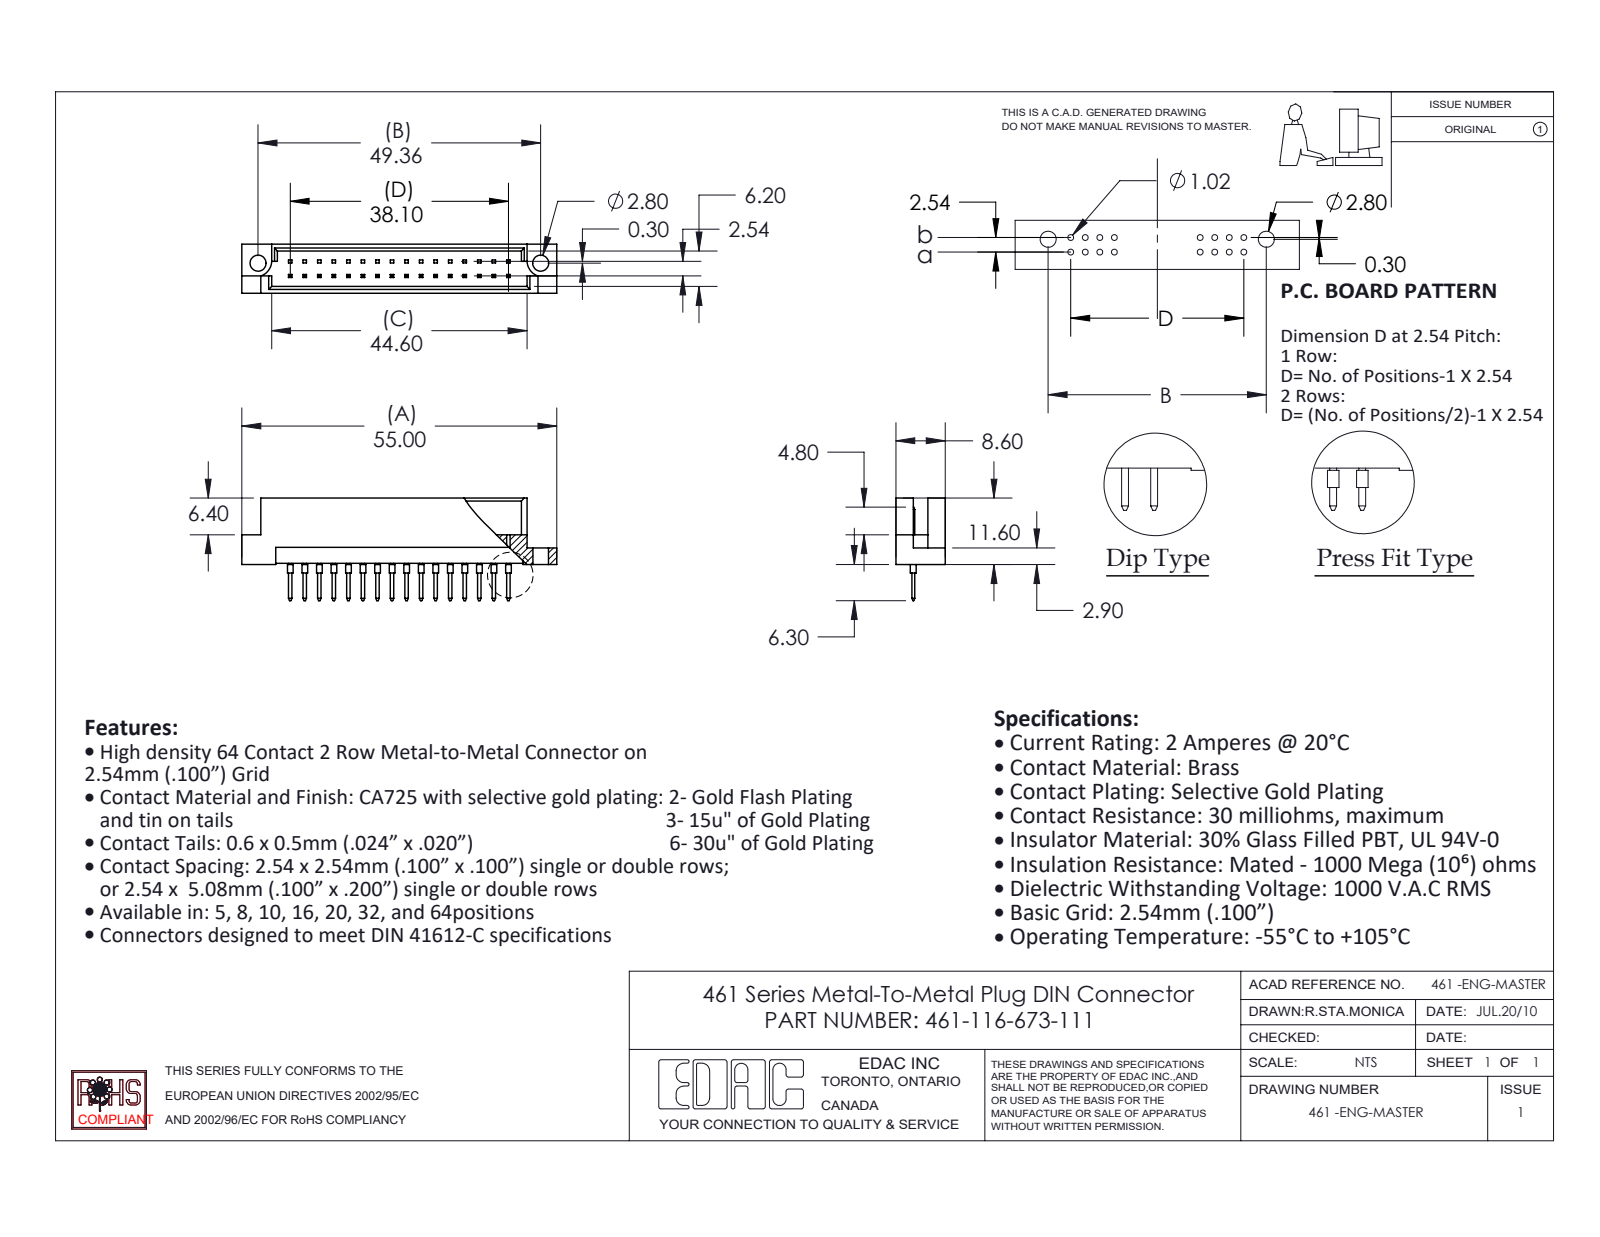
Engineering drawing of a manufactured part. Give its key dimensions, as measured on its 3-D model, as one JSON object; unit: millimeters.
{"part_name": "461-290_73; 461 Part_32; 461-116-673-111", "step_written_by": "SolidWorks 2020 (CONFIG_CONTROL_DESIGN)", "units": "millimeters", "bodies": {"solids": 17, "faces": 528, "planar": 490, "cylindrical": 38, "other": 0}, "overall_size": [55, 17.9, 8.6], "volume_mm3": 2742, "surface_area_mm2": 3854, "round_holes": [[2.8, 2]], "round_bosses_or_shafts": [[1, 16]], "partial_cylinders_radius": [[2.8, 2]], "face_to_face_distances": [1.2, 7.4, 8.6, 6.2, 2.54, 5, 2.78, 5.82, 1.58, 4.62], "hole_center_spacings": [49.36]}
